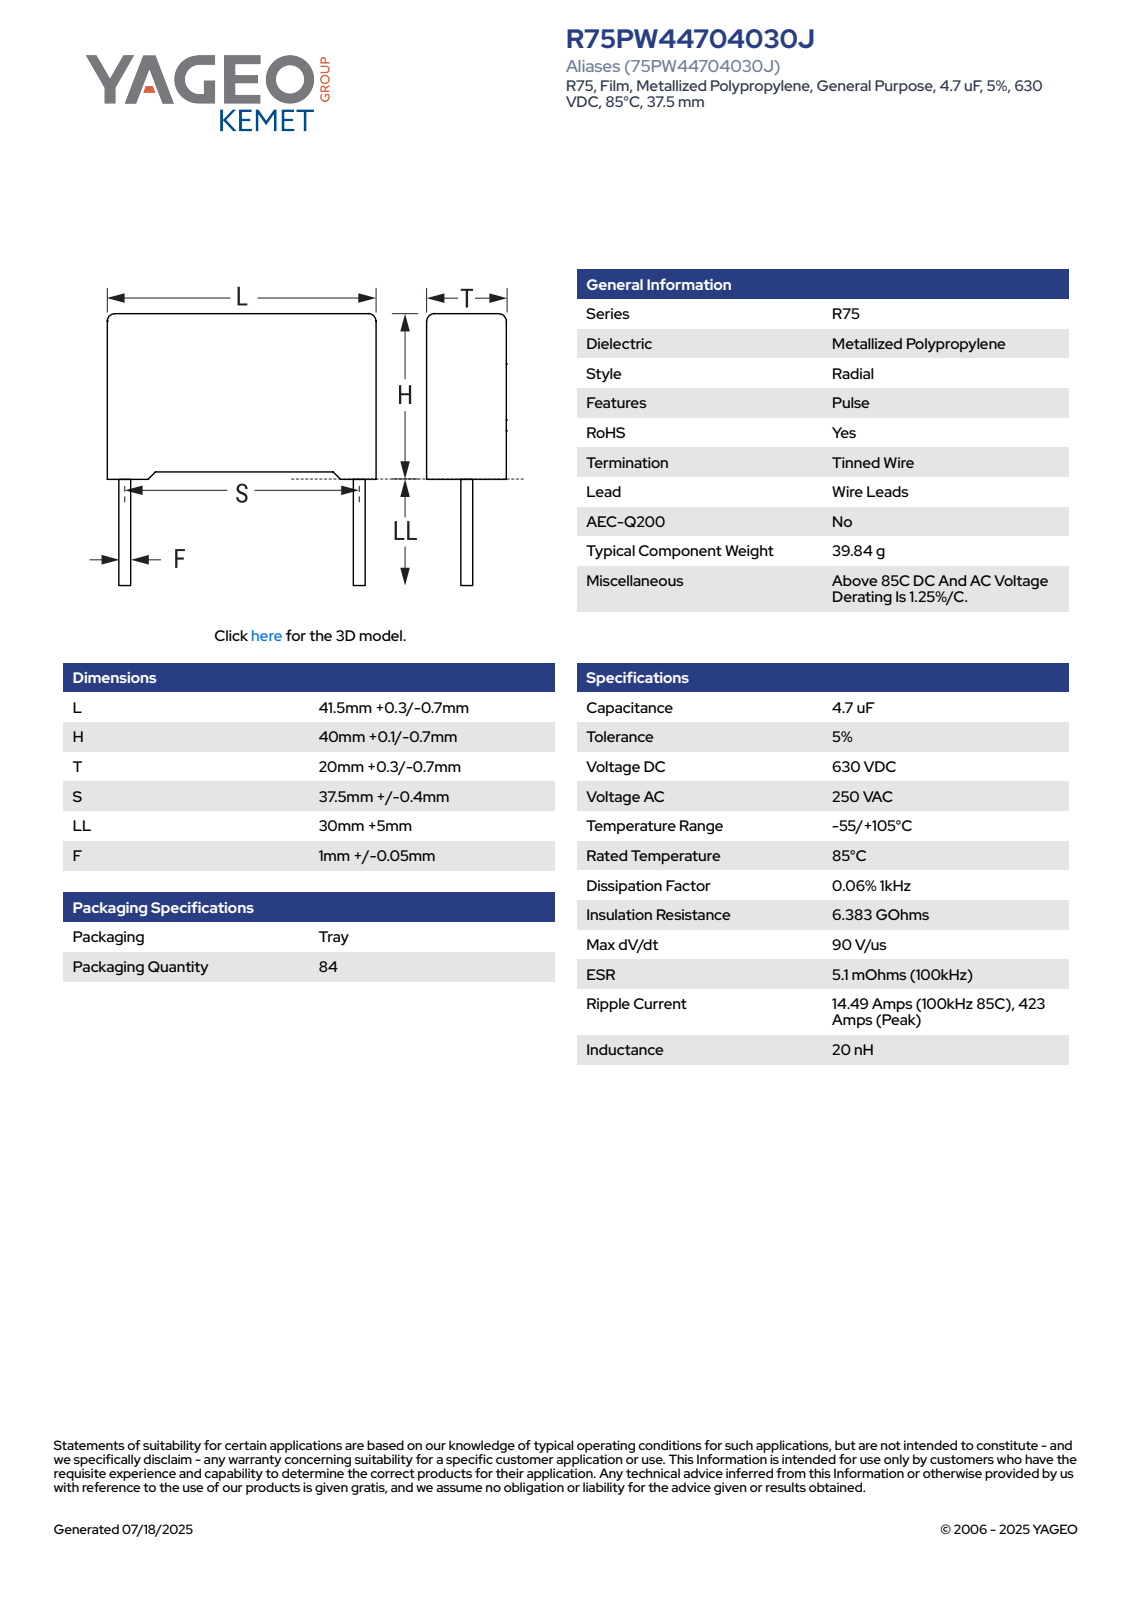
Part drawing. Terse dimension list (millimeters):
name: CFR_RB2_41.5X40X20_L41.8H40.1T20.3S37.5LL35F1.05
written by: SolidWorks 2021 (AUTOMOTIVE_DESIGN)
unit: mm
bodies: 4 solids, 85 faces (77 planar, 8 cylindrical, 0 other)
size: 75.1 × 41.8 × 20.3
volume: 33 079 mm³; area: 6 973 mm²
bosses: 2× ⌀1.05
rounds: 4× R0.5
face distances: 20.3, 41.8, 38.72, 0.63, 39.35, 0.75, 1.38, 40.1, 1.39, 20.31
